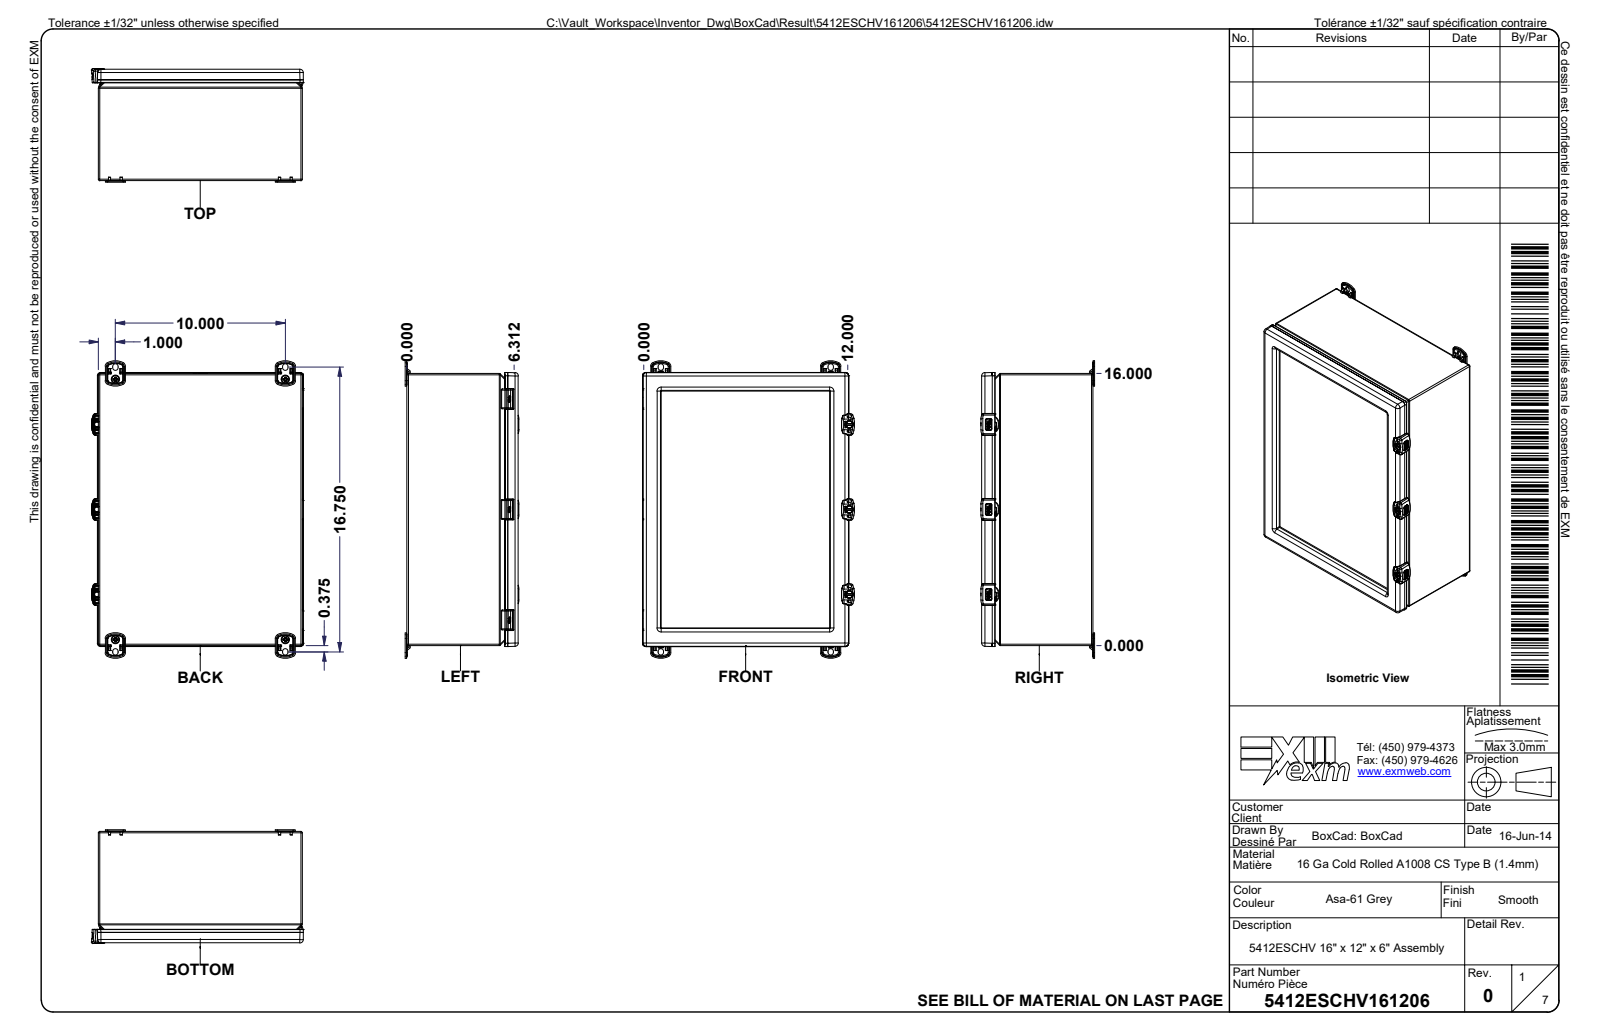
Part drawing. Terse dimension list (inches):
name: 5412ESCHV161206; 5412ESCHV161206B; 5412ESCHV161206B-P; STK-Q-08350 (+8 more)
written by: Autodesk Inventor 2024 (AUTOMOTIVE_DESIGN)
unit: in
bodies: 69 solids, 9834 faces (4136 planar, 2237 cylindrical, 3461 other)
size: 17.496 × 12.47 × 6.689
volume: 79.17 in³; area: 2 084 in²
holes: 9× ⌀0.201, 4× ⌀0.03, 4× ⌀0.24, 4× ⌀0.305, 4× ⌀0.311, 4× ⌀0.32, 3× ⌀0.165, 3× ⌀0.173, 3× ⌀0.175, 3× ⌀0.218, 3× ⌀0.236, 3× ⌀0.394
bosses: 8× ⌀0.232, 4× ⌀0.512, 4× ⌀0.39, 4× ⌀0.197, 4× ⌀0.035, 3× ⌀0.412, 3× ⌀0.33, 3× ⌀0.3
rounds: 338× R0.02, 153× R0.012, 117× R0.039, 82× R0.008, 60× R0.079, 43× R0.004, 40× R0.01, 35× R0.031
face distances: 0.053, 0.138, 11.947, 0.413, 0.467, 0.534, 0.481, 0.068, 5.939, 6.076
hole spacings: 10.139, 10.25, 0.546, 14.781, 17.916, 10, 11.417, 13.289
